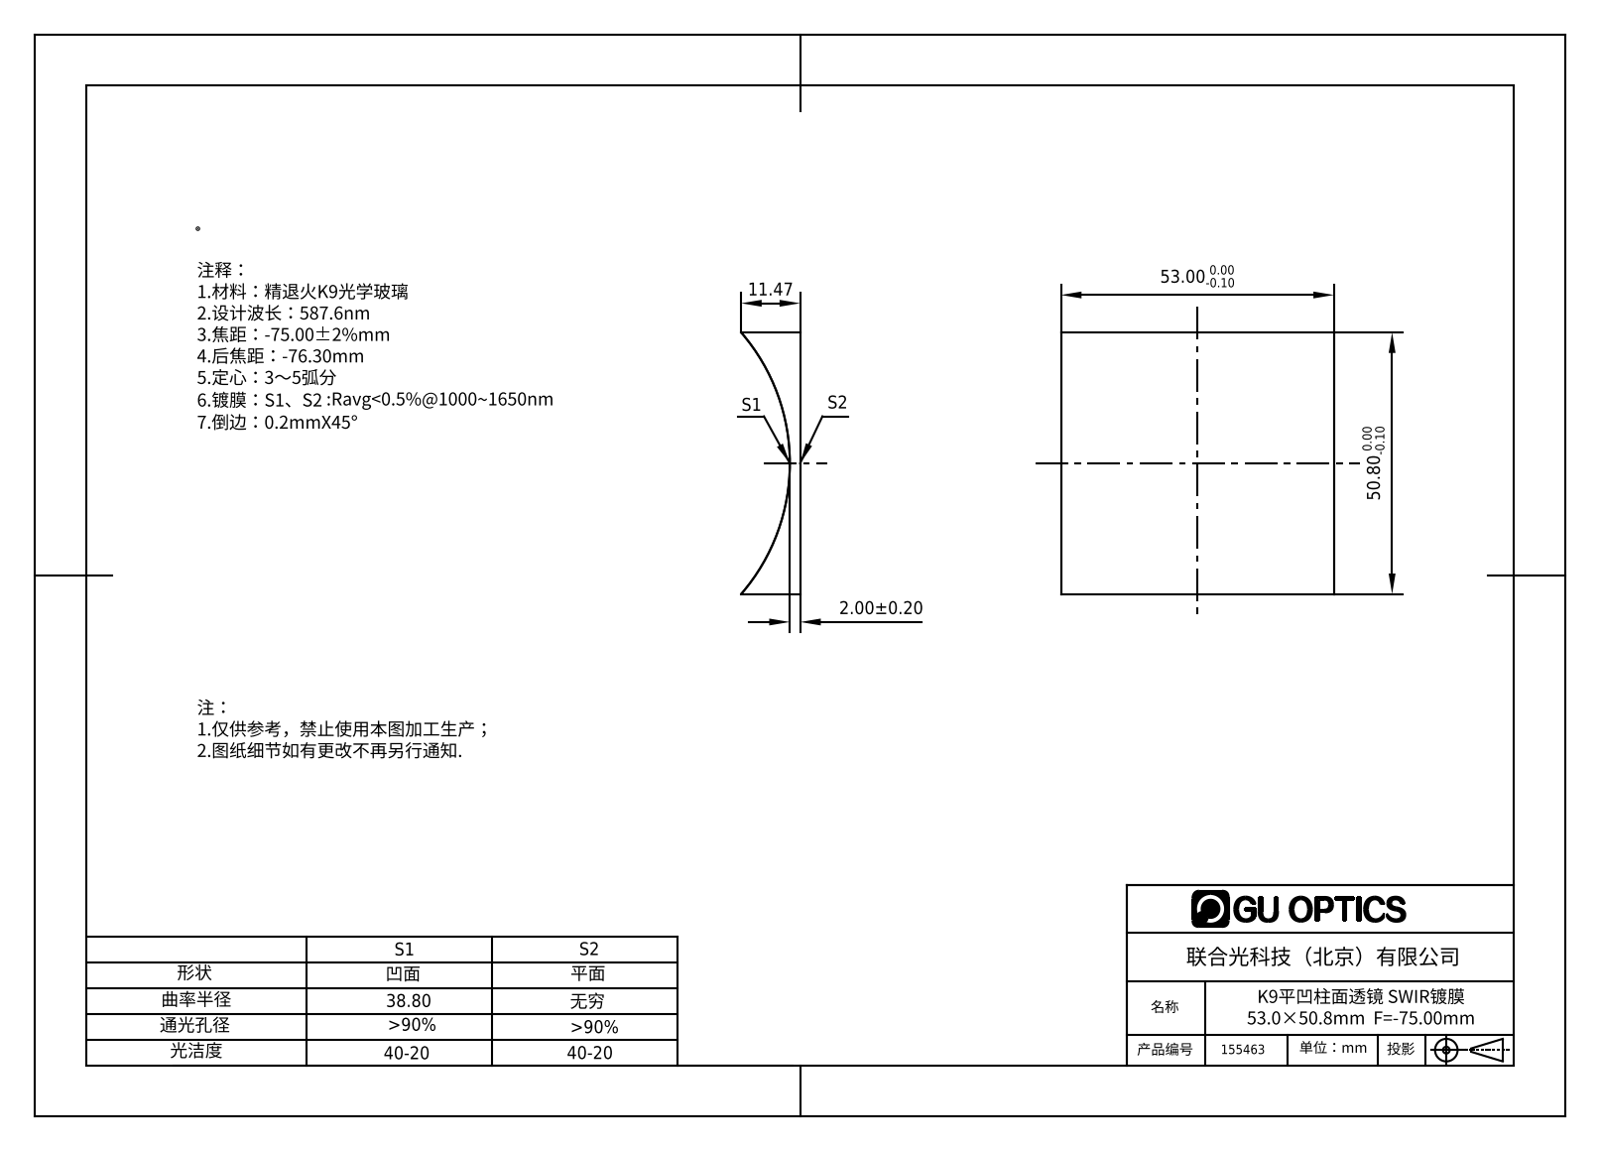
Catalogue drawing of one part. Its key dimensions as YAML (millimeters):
part_name: "155364"
step_written_by: "SolidWorks 2016 (AUTOMOTIVE_DESIGN)"
units: millimeters
bodies: {solids: 1, faces: 6, planar: 5, cylindrical: 1, other: 0}
overall_size: [53, 50.8, 11.47]
volume: 13420
surface_area: 7350
partial_cylinders:
  - {radius: 38.8, count: 1}
face_to_face_distances: [50.8, 53]
